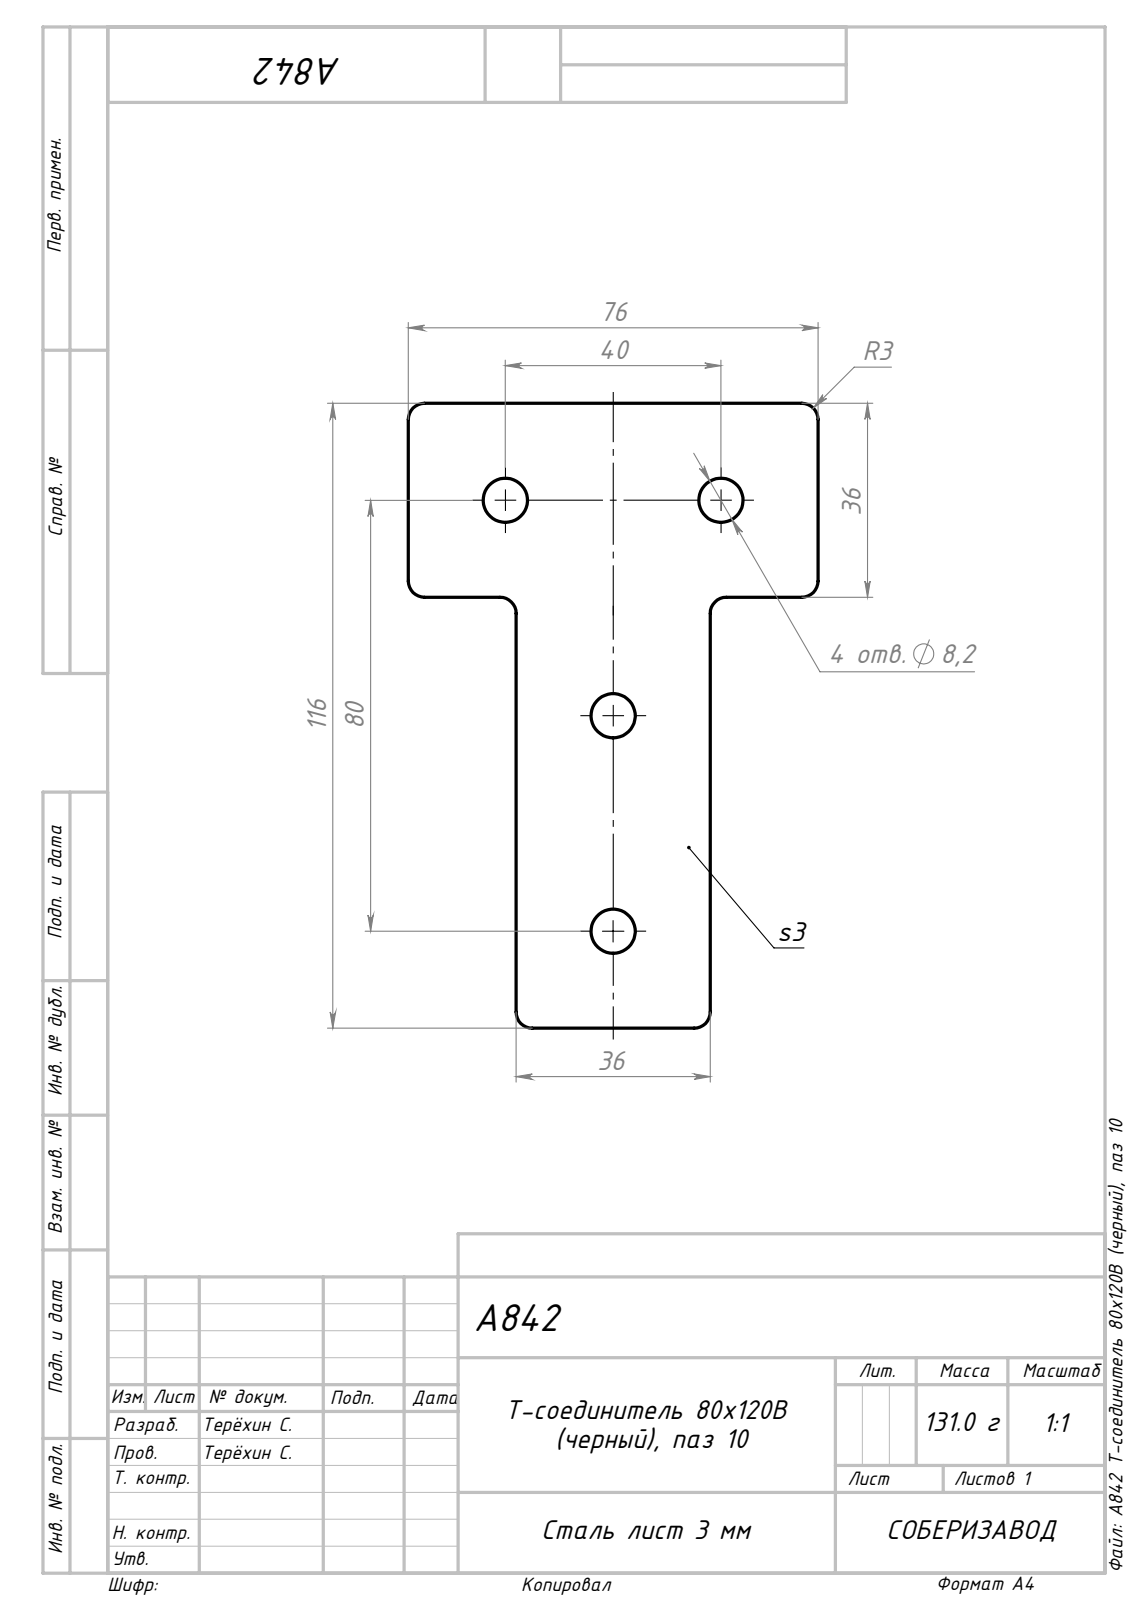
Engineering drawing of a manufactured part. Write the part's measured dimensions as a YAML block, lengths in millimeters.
part_name: "A842 Т-соединитель 80х120В (черный), паз 10_00; Сборка2"
step_written_by: "SolidWorks 2024 (AUTOMOTIVE_DESIGN)"
units: millimeters
bodies: {solids: 1, faces: 26, planar: 10, cylindrical: 16, other: 0}
overall_size: [116, 76, 3]
volume: 16191
surface_area: 12224
round_holes:
  - {diameter: 8.2, count: 4}
partial_cylinders:
  - {radius: 3, count: 8}
face_to_face_distances: [3, 36, 20, 56, 76, 116, 80]
hole_center_spacings: [40, 44.72, 82.46]
